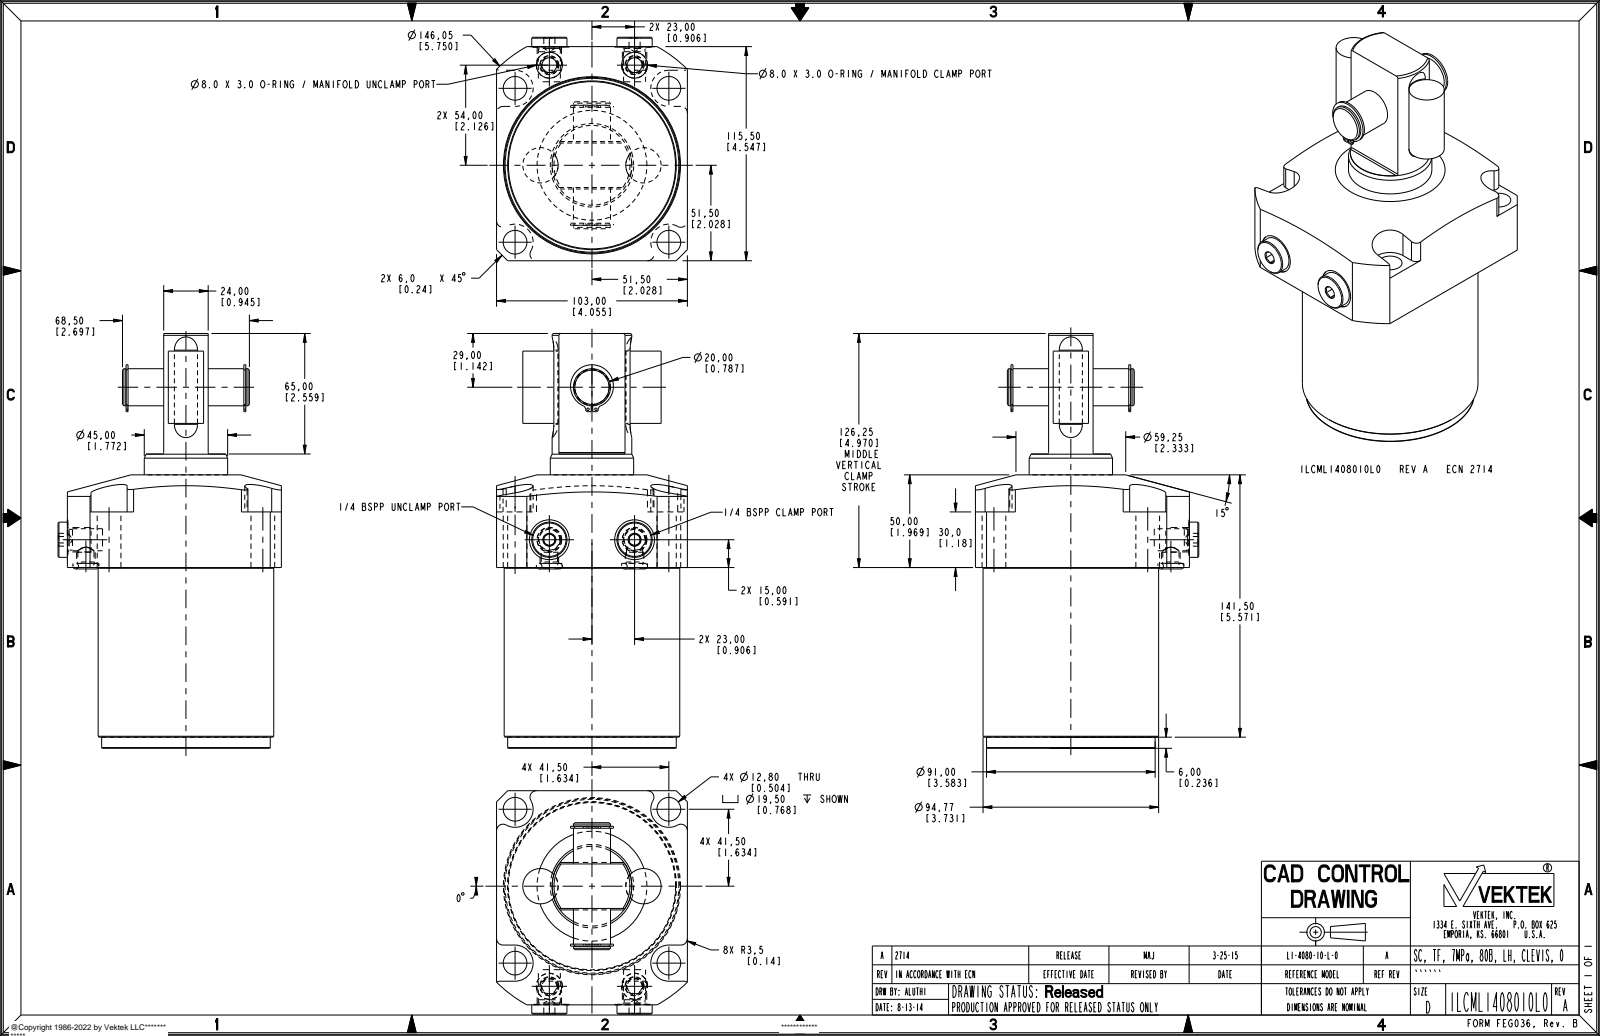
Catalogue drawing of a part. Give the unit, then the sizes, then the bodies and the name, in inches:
Units: inches
Overall size (bounding box): 8.809 × 4.746 × 4.055
Round holes (diameter × count): ⌀0.504 ×4, ⌀0.052 ×2, ⌀0.236 ×2, ⌀0.344 ×2, ⌀0.468 ×2, ⌀0.551 ×2, ⌀0.846 ×2, ⌀0.768 ×1
Round bosses / shafts (diameter × count): ⌀0.75 ×2, ⌀0.748 ×2, ⌀0.518 ×2, ⌀0.441 ×2, ⌀0.394 ×2, ⌀3.731 ×1, ⌀3.583 ×1, ⌀1.772 ×1
Partial cylindrical surfaces — rounded edges, fillets, slot ends (radius × count): R0.138 ×8, R0.384 ×4, R0.031 ×2, R0.052 ×2, R0.078 ×2, R0.375 ×2, R2.875 ×1
Main face-to-face distances: 4.055, 3.839, 4.547, 2.047, 1.555, 2.992, 2.5, 0.945, 5.807, 1.969
Hole centre spacings: 3.268, 0.475, 0.879, 1.811, 2.587, 2.89, 2.942, 3.363
Volume: 79.57 in³ · Surface area: 153.2 in²
Bodies: 5 solids, 239 faces (85 planar, 106 cylindrical, 48 other)
Part name (STEP PRODUCT): ILCML1408010L0
STEP written by: PRO/ENGINEER BY PARAMETRIC TECHNOLOGY CORPORATION, 2013320 (AUTOMOTIVE_DESIGN)
